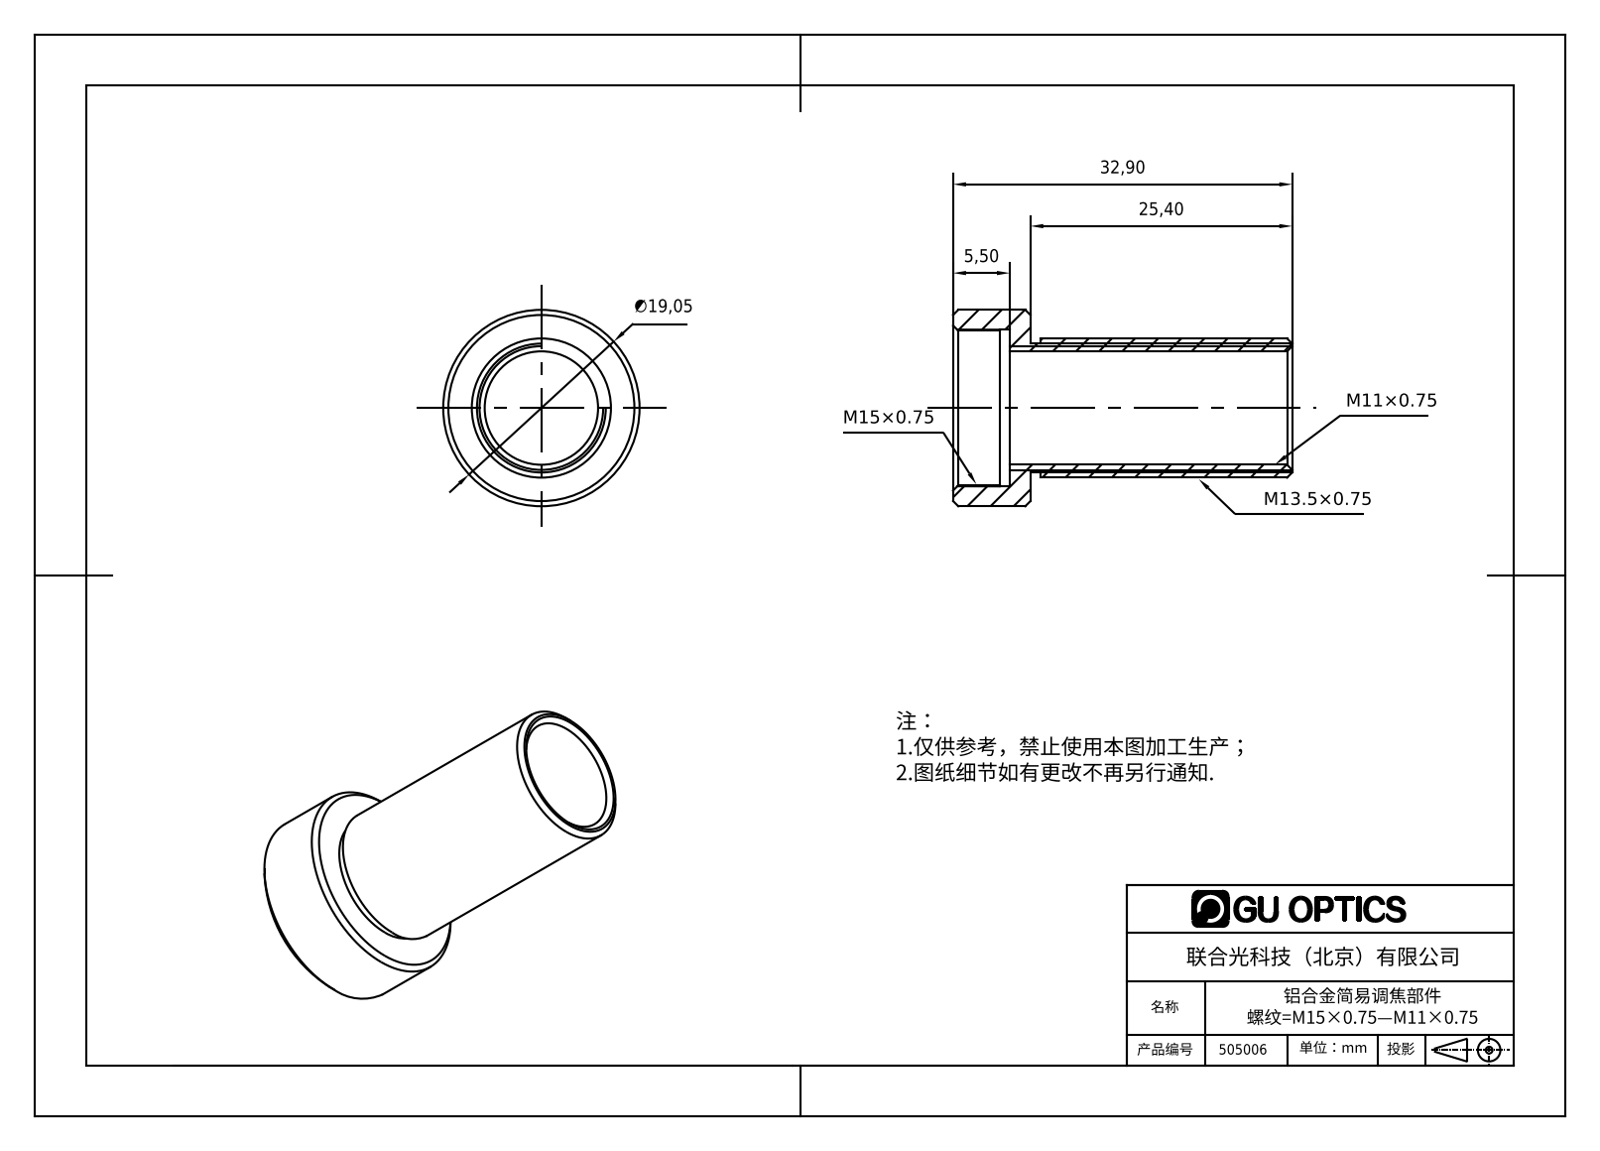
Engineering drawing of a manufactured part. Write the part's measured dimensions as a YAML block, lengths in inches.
part_name: "505006"
step_written_by: "SolidWorks 2016 (CONFIG_CONTROL_DESIGN)"
units: inches
bodies: {solids: 1, faces: 28, planar: 6, cylindrical: 12, other: 10}
overall_size: [1.295, 0.75, 0.75]
volume: 0.131
surface_area: 4.786
round_holes:
  - {diameter: 0.433, count: 1}
  - {diameter: 0.591, count: 1}
  - {diameter: 0.598, count: 1}
round_bosses_or_shafts:
  - {diameter: 0.75, count: 1}
  - {diameter: 0.531, count: 1}
  - {diameter: 0.492, count: 1}
face_to_face_distances: [0.079, 0.217, 0.295, 0.039, 0.118, 0.335, 1.295, 1.079, 1, 0.961]
